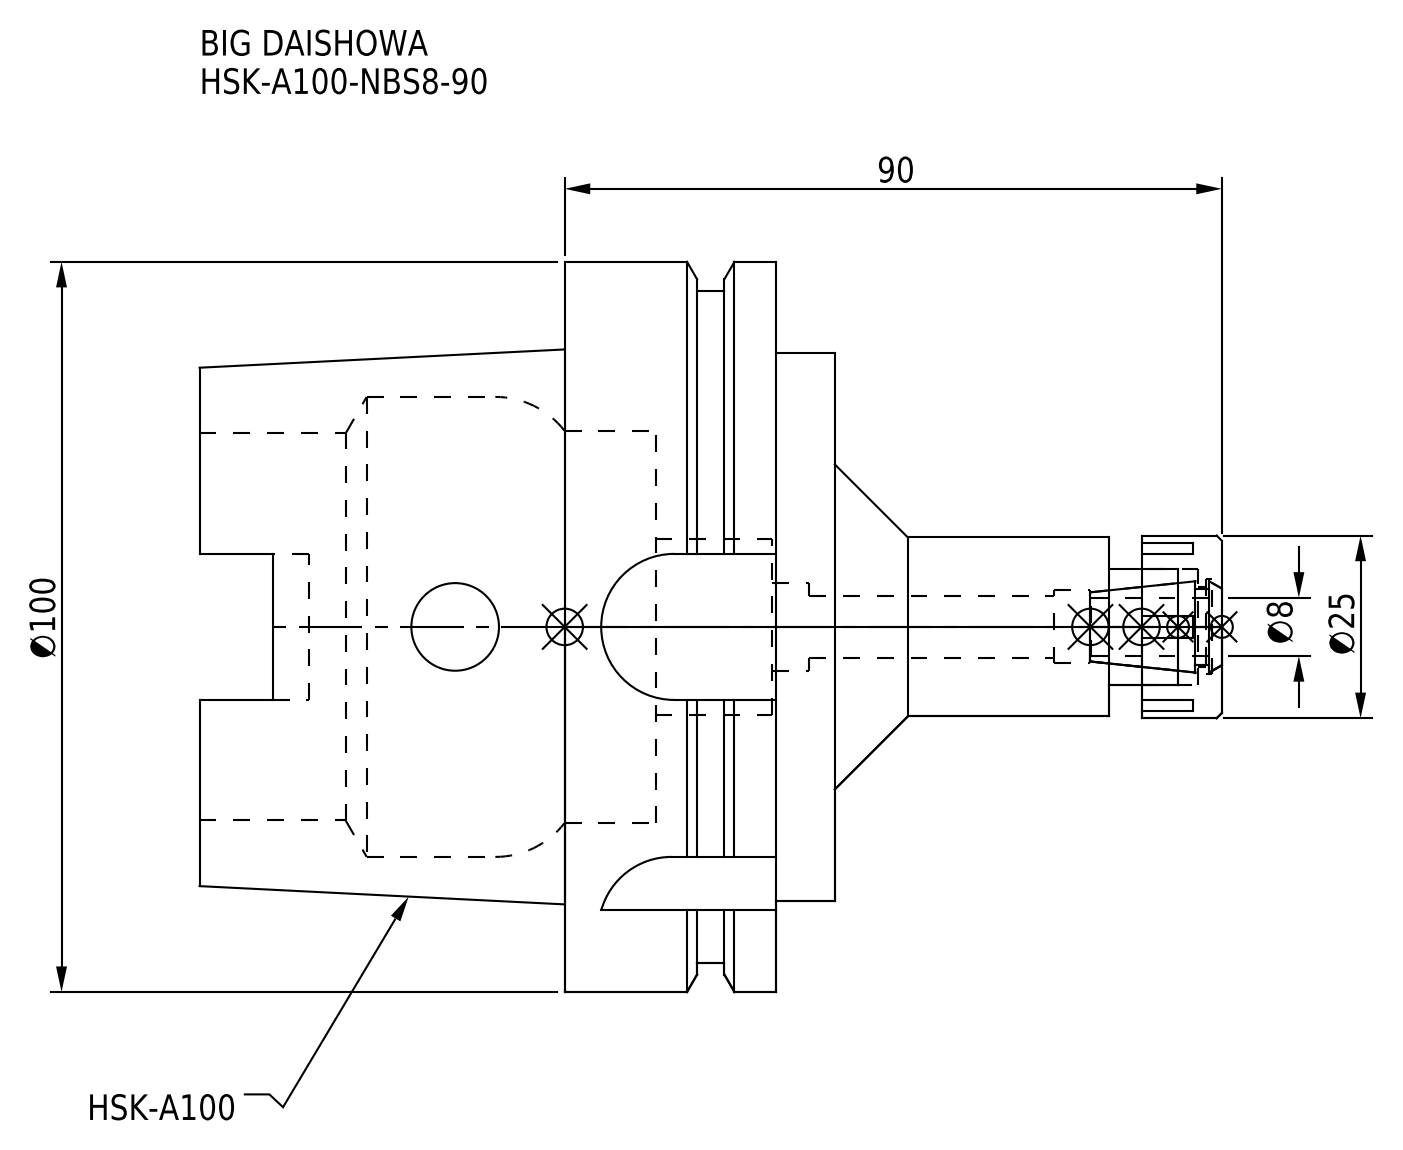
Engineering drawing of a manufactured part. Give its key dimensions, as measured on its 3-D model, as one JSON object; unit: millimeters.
{"part_name": "NBN8_1.stp; HA100NB08090-080_ASM.stp; HSK-A100-NBS8-90_1.stp; HSK-A100-NBS8-90 (+3 more)", "step_written_by": "SolidWorks 2019 (CONFIG_CONTROL_DESIGN)", "units": "millimeters", "bodies": {"solids": 2, "faces": 138, "planar": 66, "cylindrical": 50, "other": 22}, "overall_size": [140, 100, 100], "volume_mm3": 312840, "surface_area_mm2": 58751, "round_holes": [[12, 2], [8.4, 1], [10, 1], [11, 1], [13, 1], [16, 1], [24, 1], [53, 1], [53.8, 1], [63, 1]], "round_bosses_or_shafts": [[100, 1], [92, 1], [75, 1], [25, 1], [24.5, 1]], "partial_cylinders_radius": [[4.88, 4], [10, 4]], "face_to_face_distances": [29, 8, 37, 24.55, 16.55, 12.45, 50, 79, 87, 62.45]}
